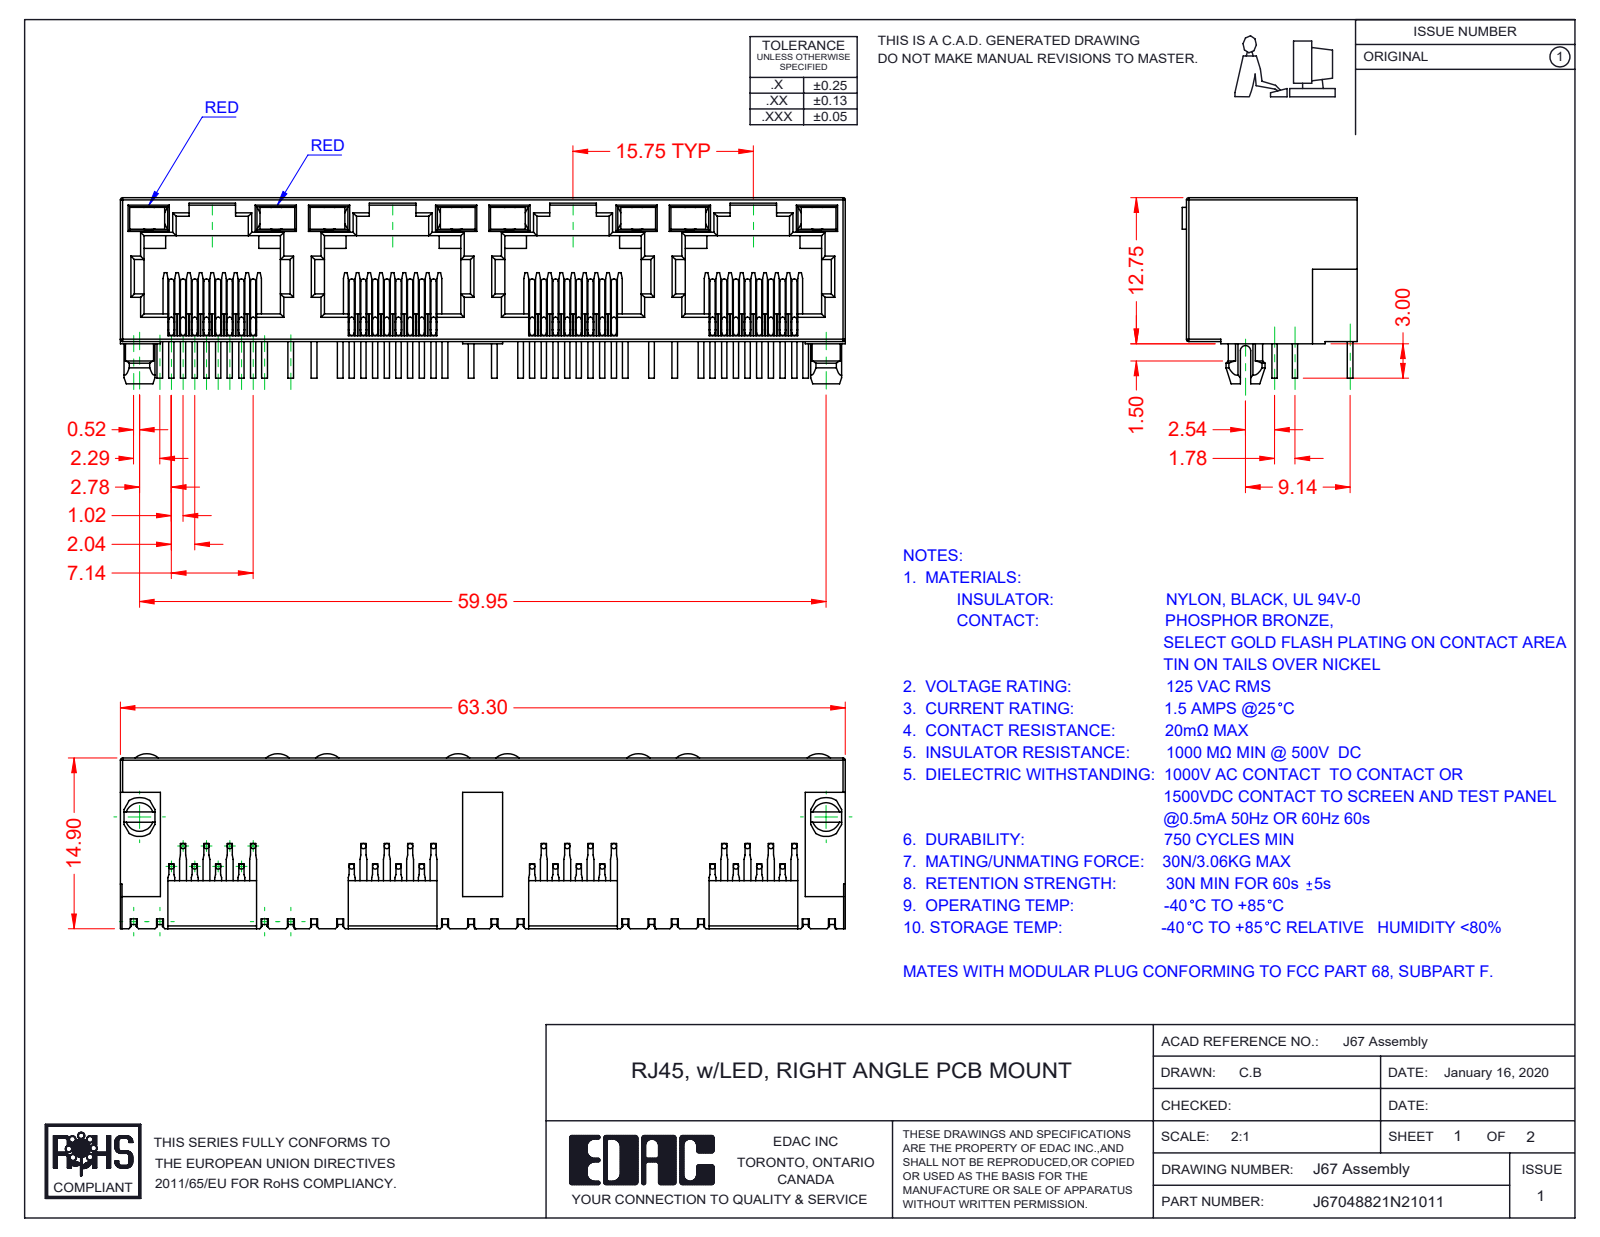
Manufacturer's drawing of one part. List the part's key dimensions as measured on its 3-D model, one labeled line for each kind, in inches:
Part name (STEP PRODUCT): J67048822N22011; 67 LED LH_2-Red; 67 Insulator; 67 LED RH_2-Red (+1 more)
STEP written by: SolidWorks 2016 (CONFIG_CONTROL_DESIGN)
Units: inches
Bodies: 41 solids, 2465 faces (1781 planar, 476 cylindrical, 208 other)
Overall size (bounding box): 2.492 × 0.64 × 0.602
Volume: 0.315 in³ · Surface area: 17.94 in²
Round bosses / shafts (diameter × count): ⌀0.018 ×96
Partial cylindrical surfaces — rounded edges, fillets, slot ends (radius × count): R0.008 ×66, R0.012 ×29, R0.018 ×9, R0.061 ×8, R0.059 ×2, R0.067 ×2, R0.014 ×1, R0.039 ×1
Main face-to-face distances: 0.02, 0.494, 0.074, 0.035, 0.394, 0.62, 0.039, 0.055, 0.433, 0.468
